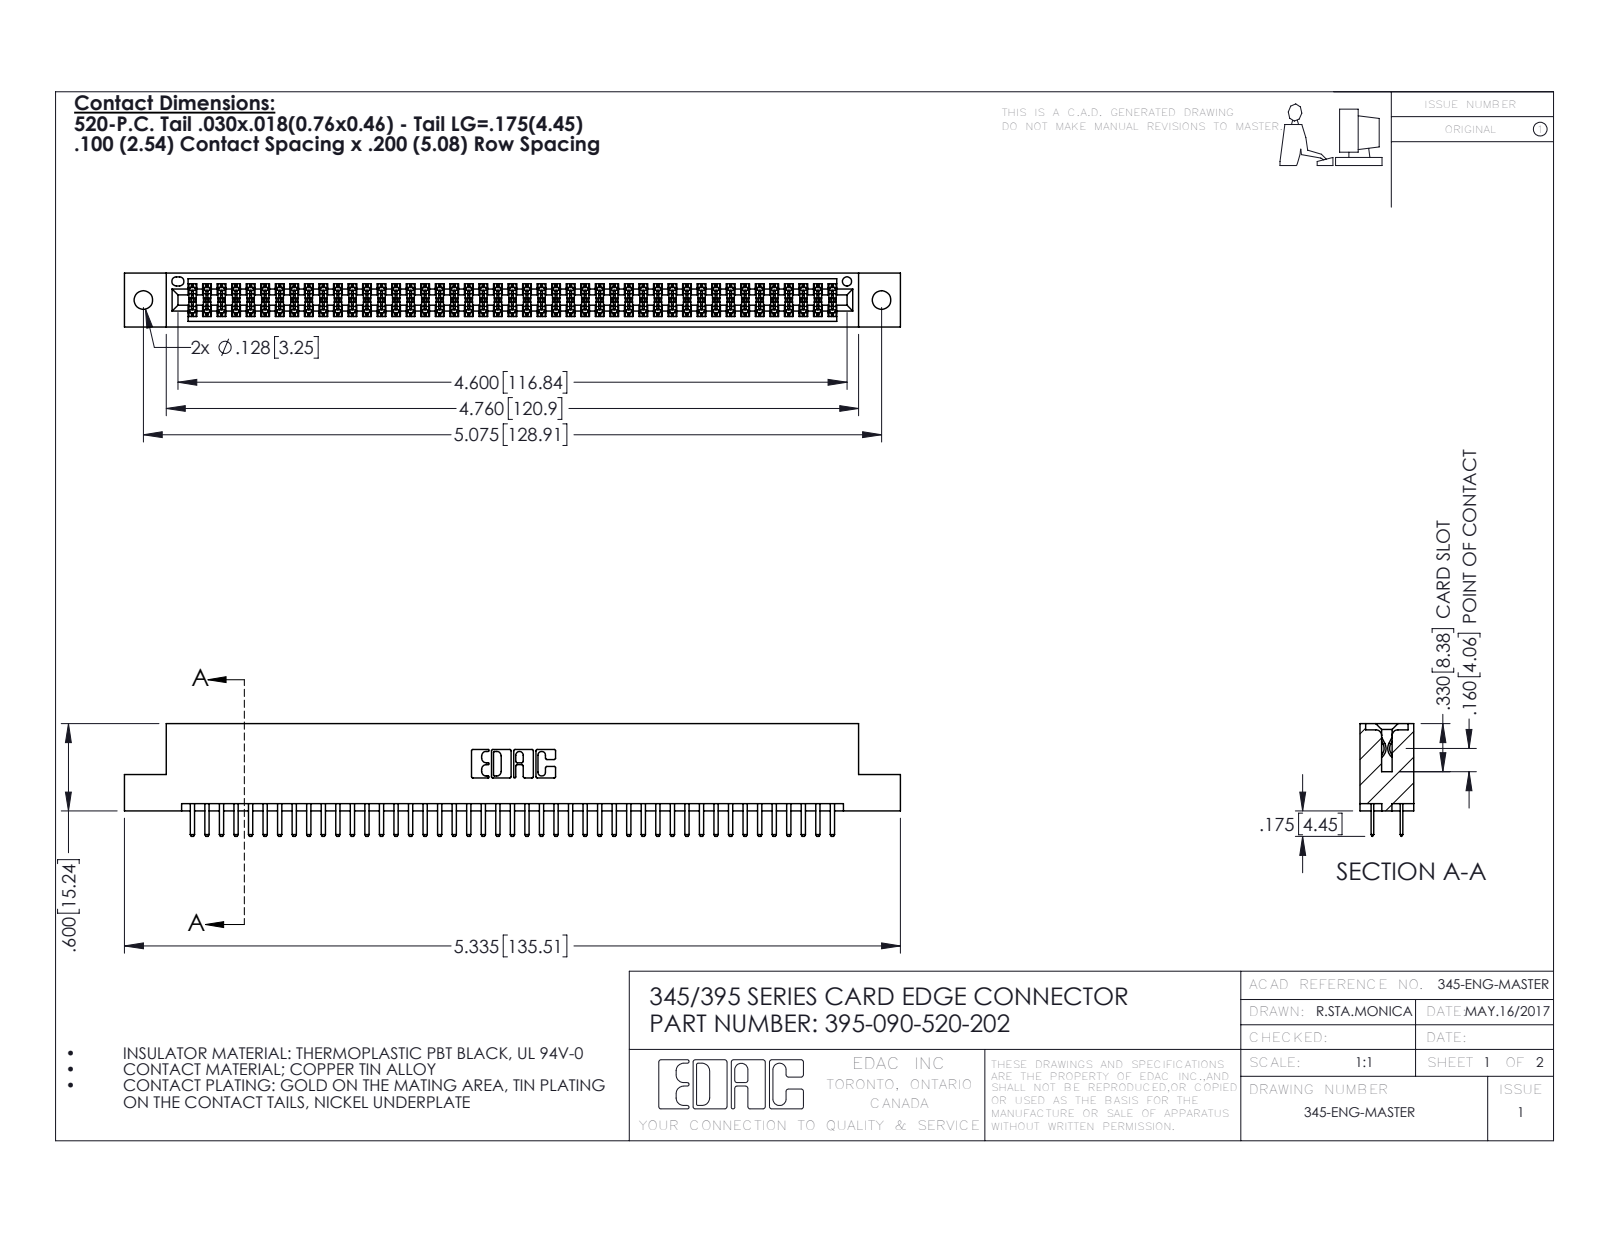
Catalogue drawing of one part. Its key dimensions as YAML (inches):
part_name: "345 Part_Flush Mounting Lugs - 0.128 Dia; 395-090-520-202; 345-292-001_345-293-120"
step_written_by: "SolidWorks 2016 (CONFIG_CONTROL_DESIGN)"
units: inches
bodies: {solids: 91, faces: 4986, planar: 3230, cylindrical: 1756, other: 0}
overall_size: [5.335, 0.775, 0.37]
volume: 0.8
surface_area: 29.59
round_holes:
  - {diameter: 0.128, count: 2}
  - {diameter: 0.064, count: 1}
partial_cylinders:
  - {radius: 0.006, count: 135}
  - {radius: 0.01, count: 94}
  - {radius: 0.01, count: 22}
  - {radius: 0.007, count: 6}
  - {radius: 0.031, count: 6}
  - {radius: 0.026, count: 3}
  - {radius: 0.014, count: 2}
  - {radius: 0.019, count: 2}
face_to_face_distances: [0.298, 0.072, 0.2, 0.37, 0.098, 0.272, 0.025, 0.225, 0.022, 0.072]
hole_center_spacings: [0.27, 4.839, 5.075]
